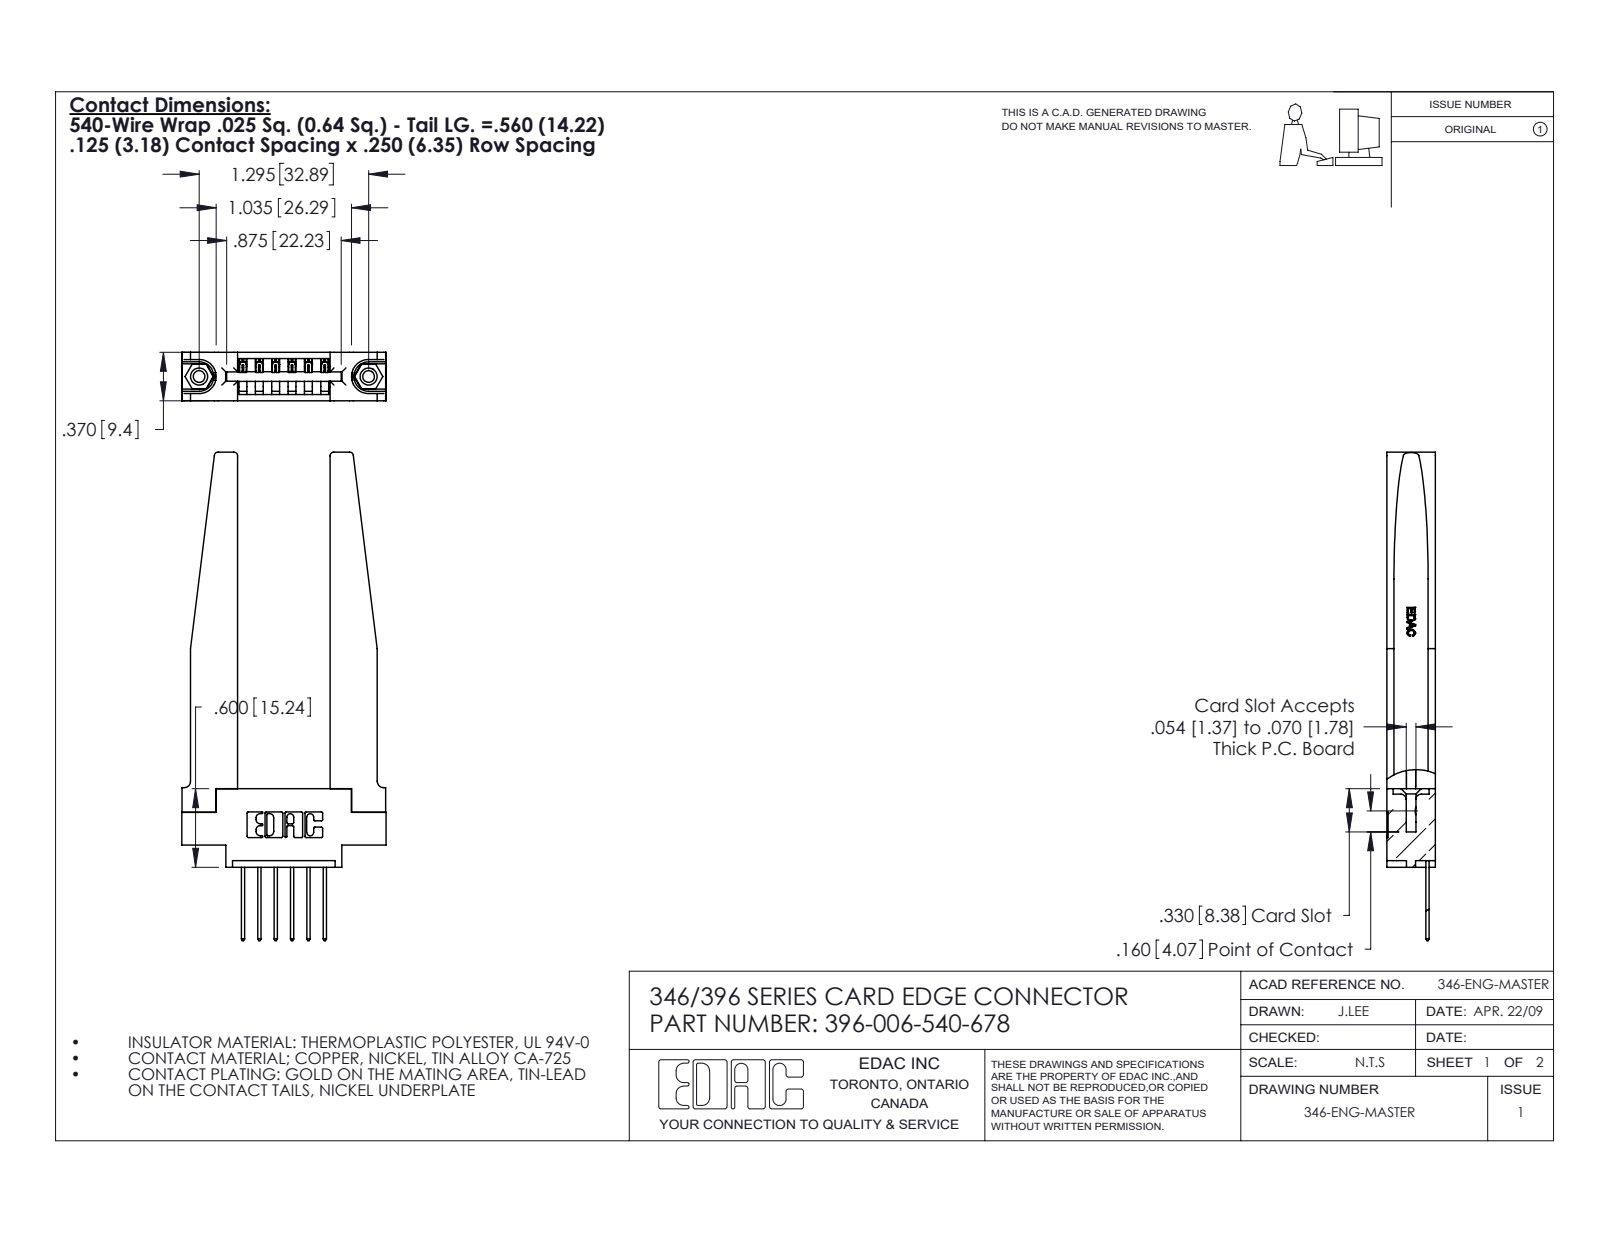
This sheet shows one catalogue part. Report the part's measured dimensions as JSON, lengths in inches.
{"part_name": "346 Part_0.170 Offset - 0.156 Dia-TH; 345-292-001_345-293-140; 346-220-078_345-220-078; 345-250-001_345-250-001-102 (+1 more)", "step_written_by": "SolidWorks 2020 (CONFIG_CONTROL_DESIGN)", "units": "inches", "bodies": {"solids": 11, "faces": 722, "planar": 476, "cylindrical": 194, "other": 52}, "overall_size": [3.73, 1.56, 0.37], "volume_in3": 0.628, "surface_area_in2": 16.47, "round_holes": [[0.089, 2], [0.125, 2], [0.156, 2], [0.064, 1]], "round_bosses_or_shafts": [[0.155, 2]], "partial_cylinders_radius": [[0.01, 22], [0.006, 12], [0.01, 12], [0.03, 8], [0.007, 6], [0.031, 6], [0.026, 3], [0.031, 2]], "face_to_face_distances": [0.37, 0.15, 0.22, 0.25, 0.706, 0.072, 0.148, 0.102, 0.048, 0.322], "hole_center_spacings": [0.246, 1.092, 1.295]}
